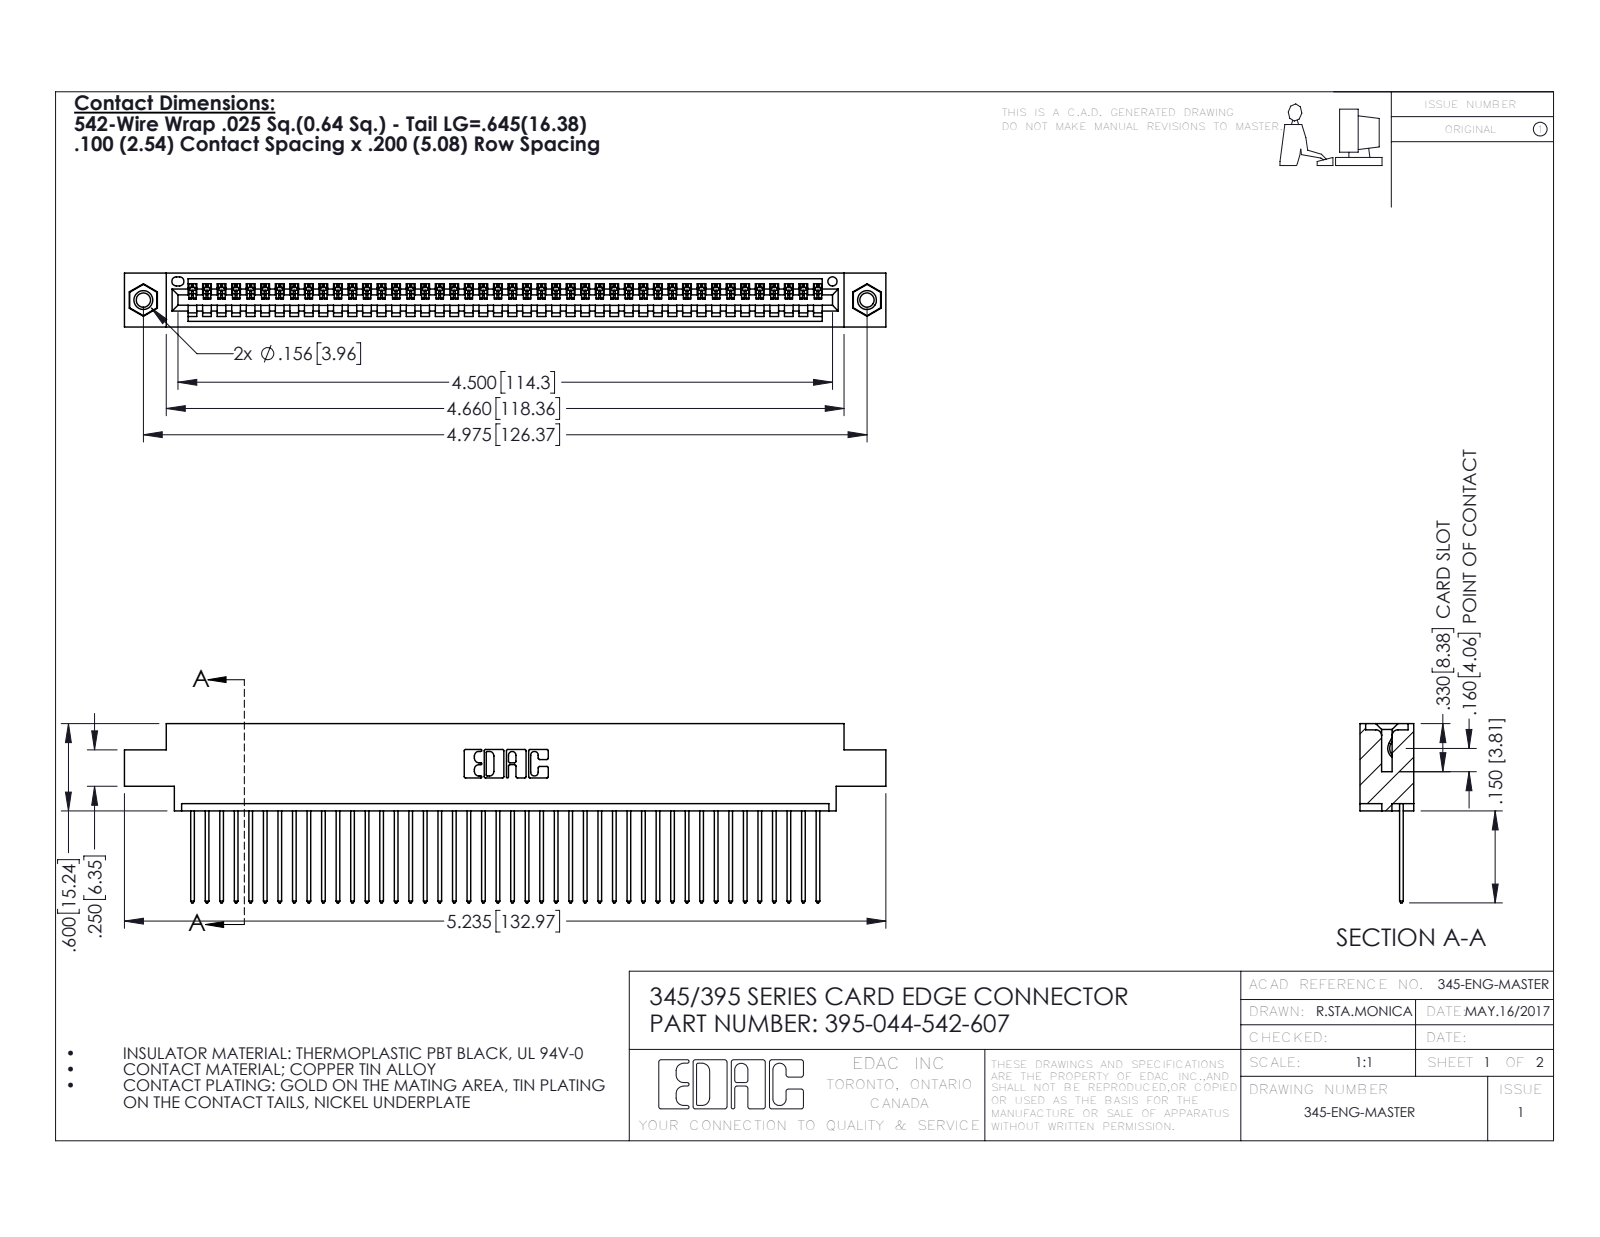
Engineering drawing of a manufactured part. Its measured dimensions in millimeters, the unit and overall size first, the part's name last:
Units: millimetres
Overall size (bounding box): 133 × 31.3 × 9.4
Round holes (diameter × count): ⌀2.5 ×2, ⌀3.2 ×2, ⌀4 ×2, ⌀1.6 ×1
Round bosses / shafts (diameter × count): ⌀3.9 ×2
Partial cylindrical surfaces — rounded edges, fillets, slot ends (radius × count): R0.2 ×88, R0.3 ×88, R0.3 ×22, R0.2 ×6, R0.8 ×6, R0.7 ×3, R0.8 ×2, R1 ×2
Main face-to-face distances: 1.8, 7.6, 9.4, 2.5, 6.9, 0.6, 5.1, 5.7, 4.4, 3.8
Hole centre spacings: 6.9, 120.4, 126.4
Volume: 12 600 mm³ · Surface area: 17 570 mm²
Bodies: 47 solids, 2742 faces (1876 planar, 850 cylindrical, 16 other)
Part name (STEP PRODUCT): 395-044-542-607; 345 Part_0.170 Offset - 0.156 Dia-TI; 345-292-001_345-293-142; 345-250-001_345-250-005-103
STEP written by: SolidWorks 2016 (CONFIG_CONTROL_DESIGN)
